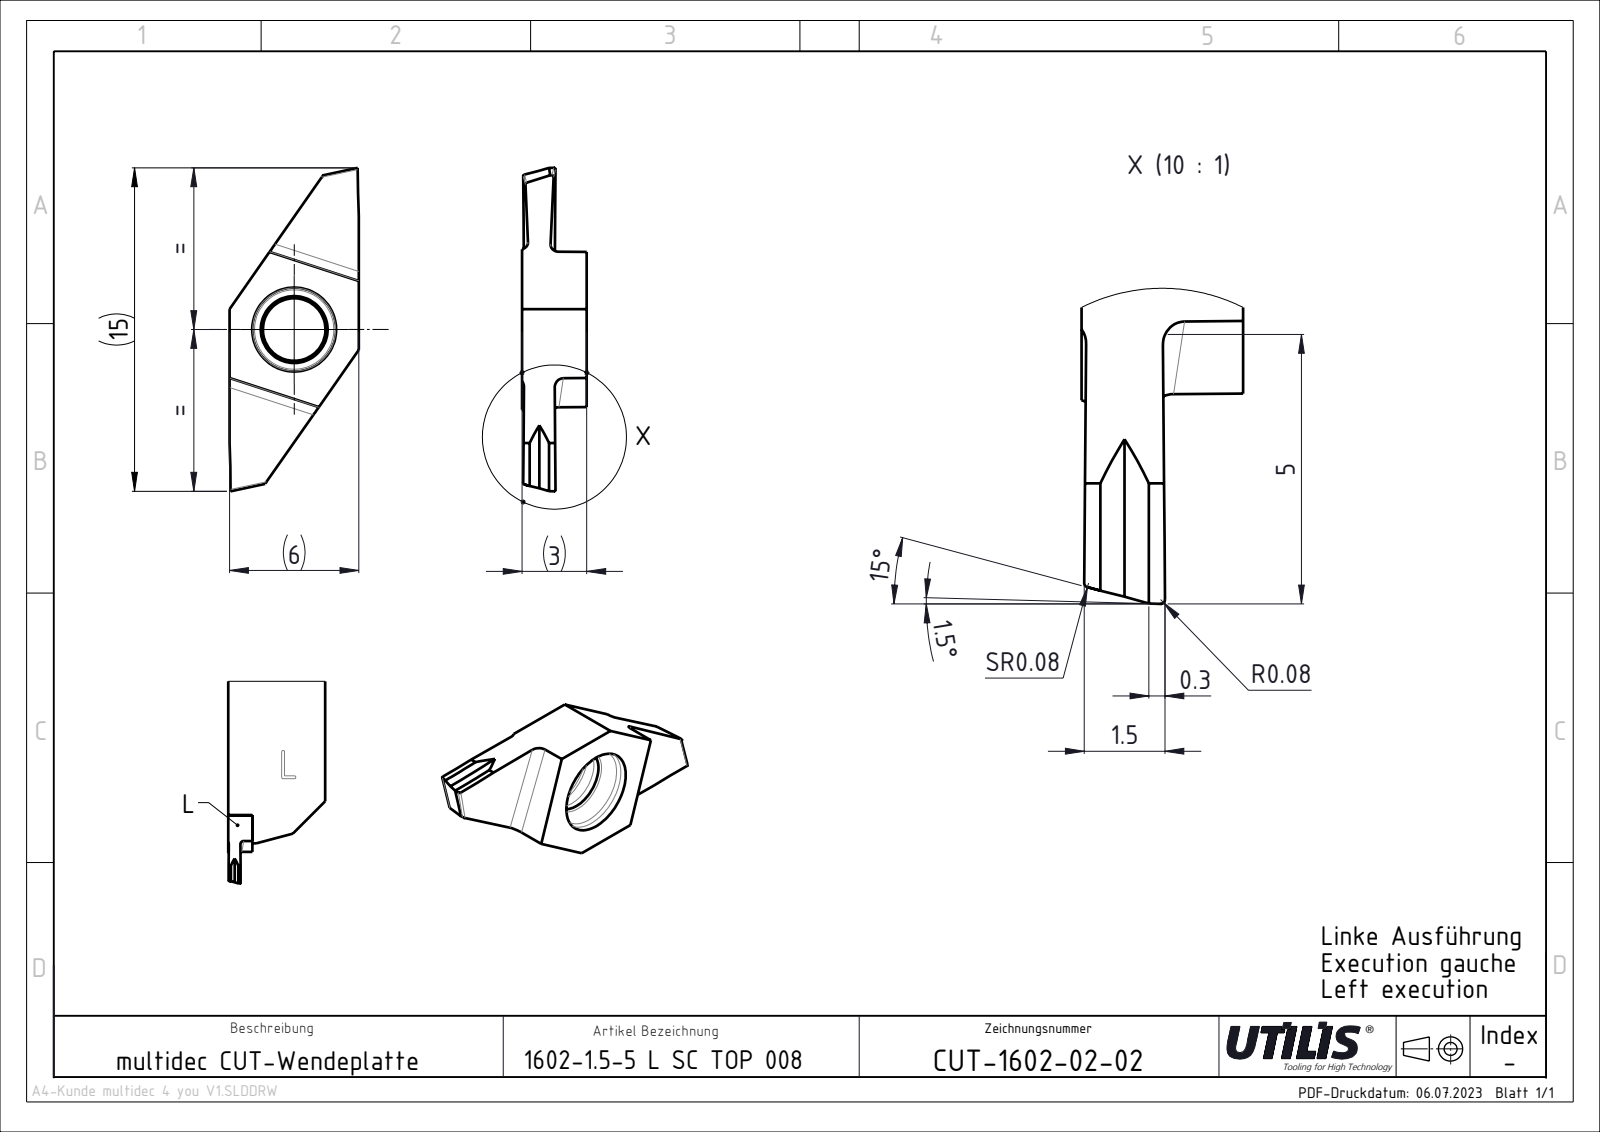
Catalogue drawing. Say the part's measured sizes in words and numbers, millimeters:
The part is named "1602-CUT-1602-02-02 stp". Its 3-D file was written by "SolidWorks 2022 (AUTOMOTIVE_DESIGN)". It is 1 solid with 27 faces: 18 planar, 9 cylindrical and 0 other. Overall it measures 15 by 6 by 3 millimeters. Its volume is 118 cubic millimeters and its surface area 216 square millimeters. Round holes: 1 of diameter 2.9. Partial cylindrical surfaces (rounded edges, fillets, slot ends): 4 of radius 0.4. The main face-to-face distances are 6, 3, 1.35, 15.
